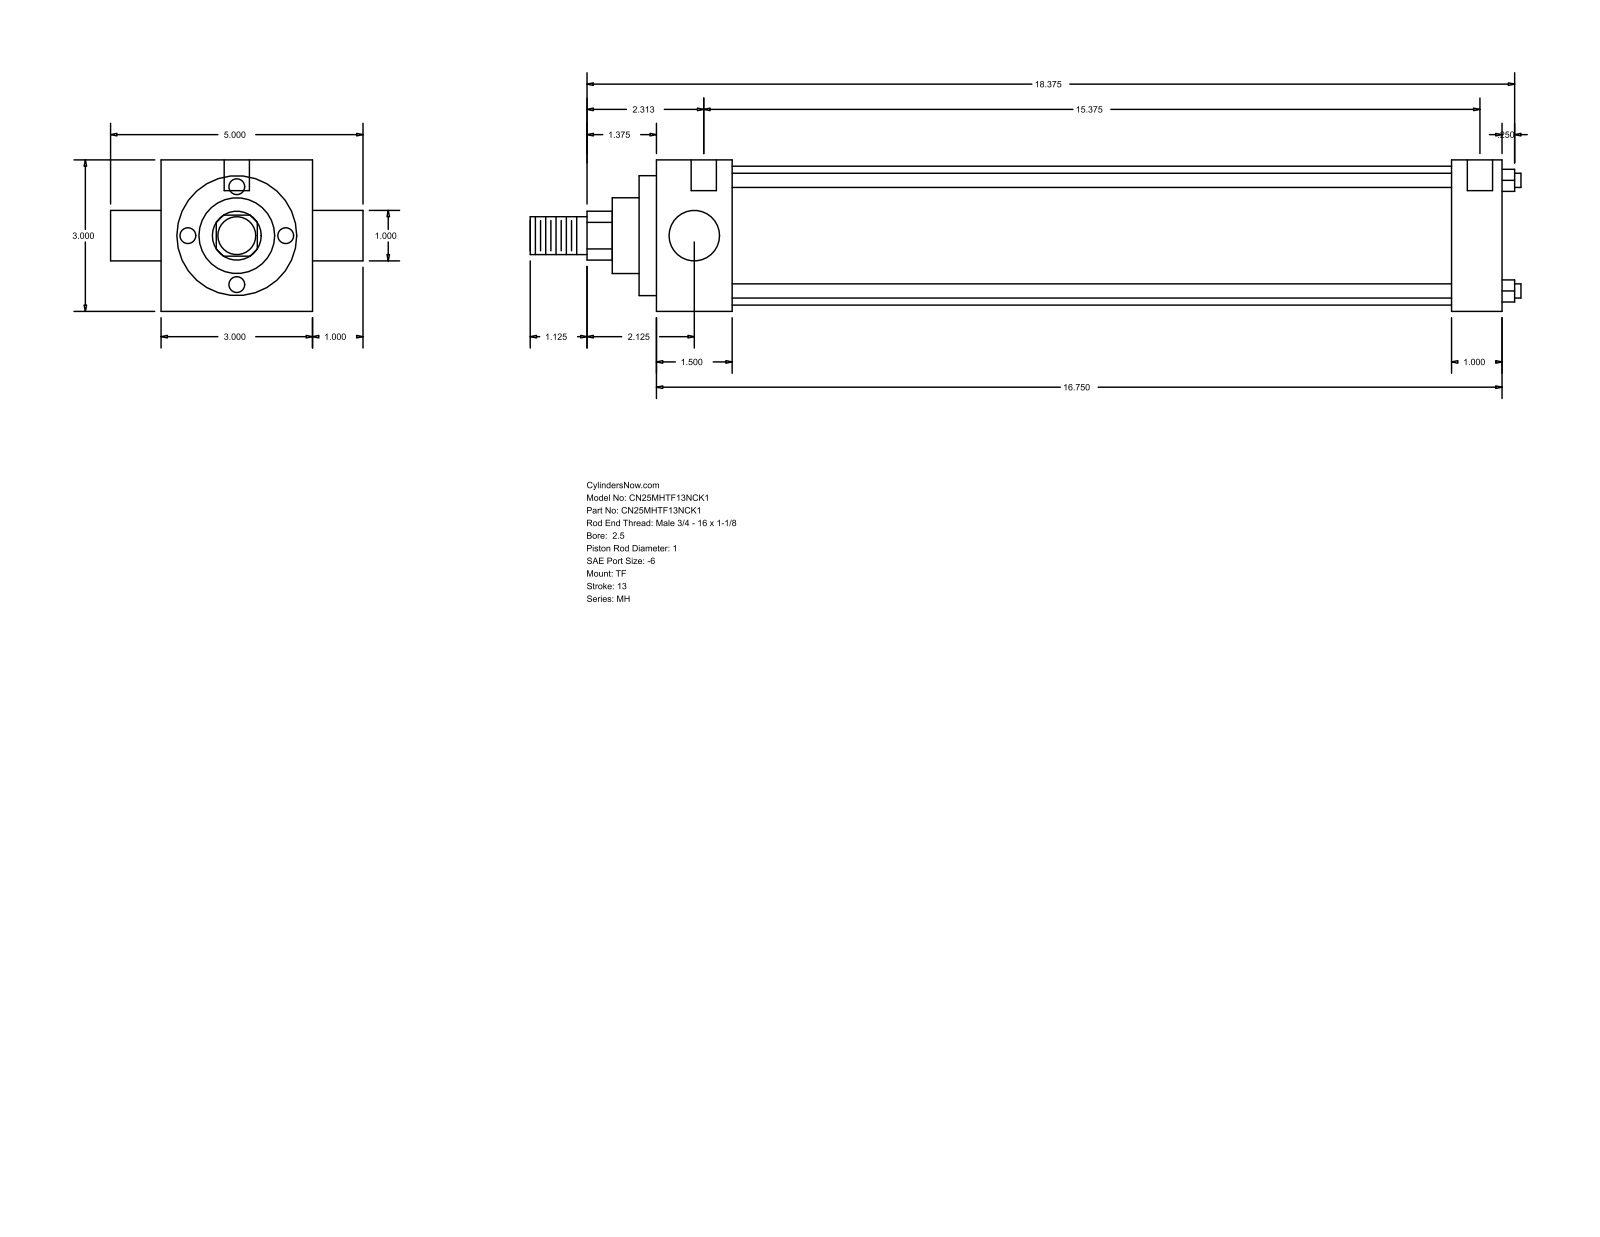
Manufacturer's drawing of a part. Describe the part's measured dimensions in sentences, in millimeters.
The part is named "MH_TF__0250_1". Its 3-D file was written by "GSSL Pune (CONFIG_CONTROL_DESIGN)". It is 0 solids with 86 faces: 61 planar, 25 cylindrical and 0 other. Overall it measures 498.48 by 127 by 76.2 millimeters. Round holes: 3 of diameter 5.56, 2 of diameter 12.7. Round bosses or shafts: 4 of diameter 7.14, 2 of diameter 25.4, 1 of diameter 69.85, 1 of diameter 60.33, 1 of diameter 38.1, 1 of diameter 19.05. Partial cylindrical surfaces (rounded edges, fillets, slot ends): 1 of radius 12.29. The main face-to-face distances are 76.2, 425.46, 25.4, 38.11, 387.35, 400.06, 361.95, 8.73, 46.84, 408.79. The hole center spacings are 3.18, 4.76, 390.52, 393.7, 395.28, 398.46.
